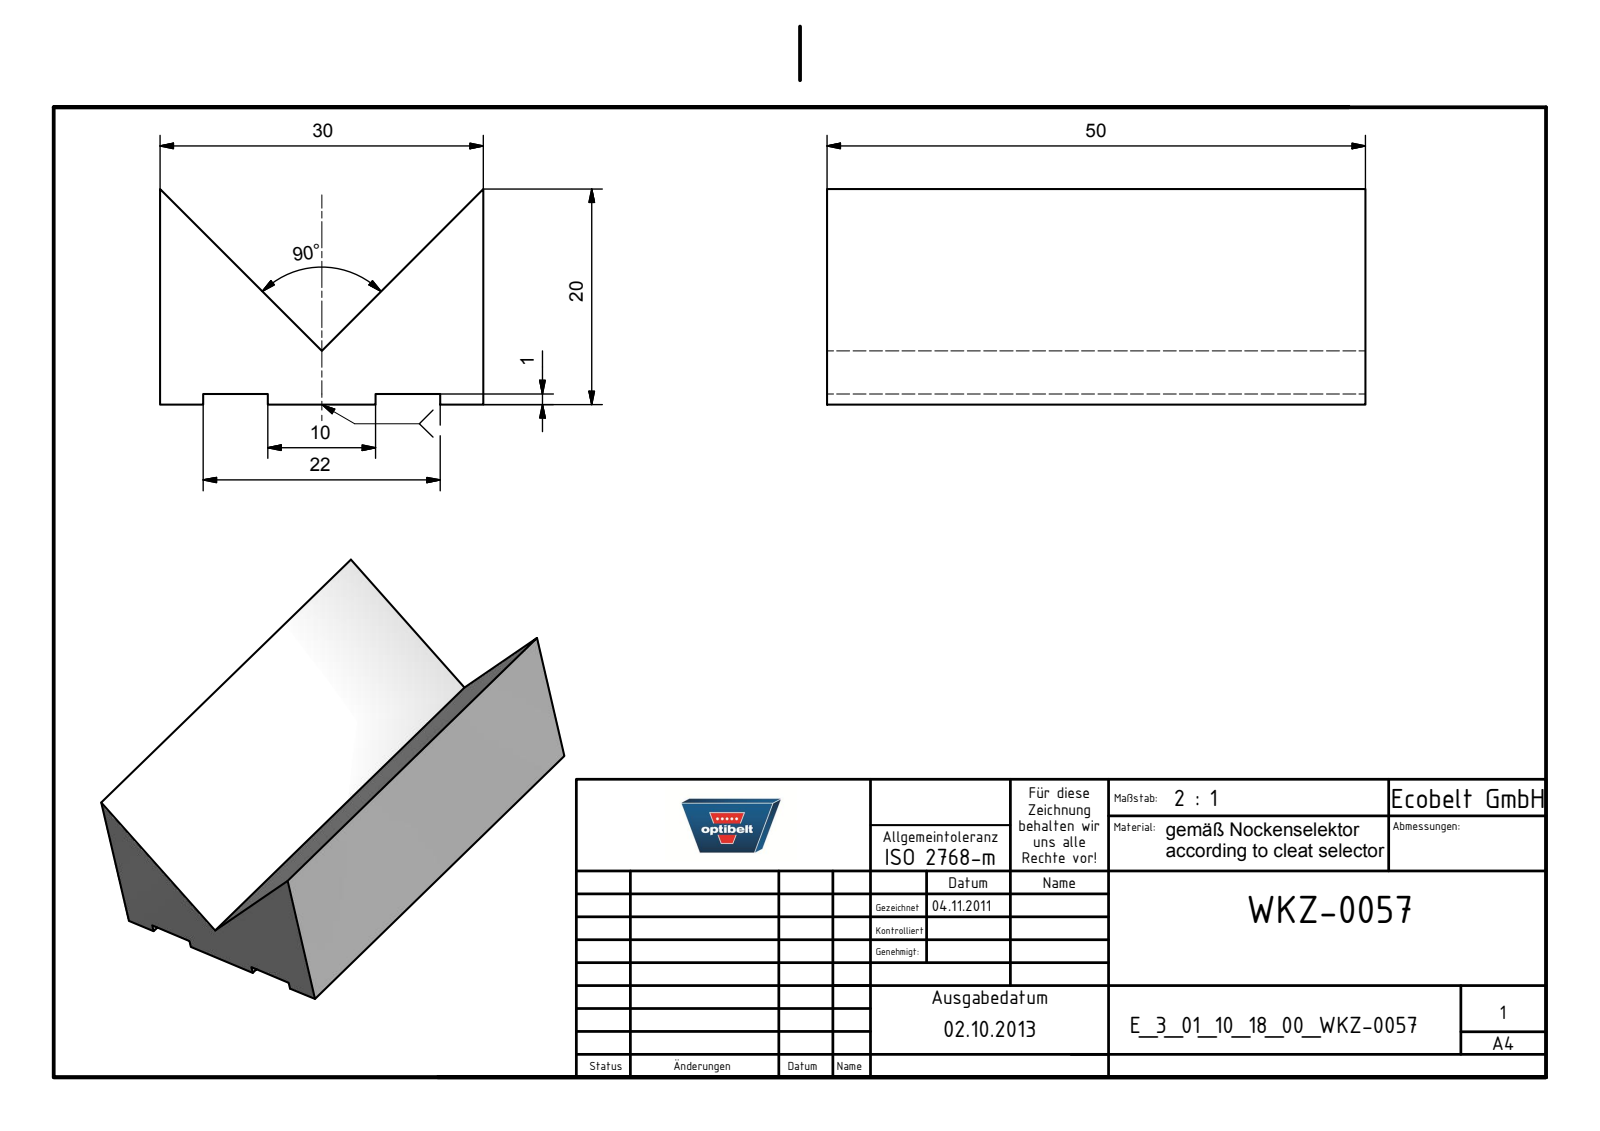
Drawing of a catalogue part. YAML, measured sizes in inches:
part_name: "E_3_01_10_18_00_WKZ-0057"
step_written_by: "Autodesk Inventor 2025 (AUTOMOTIVE_DESIGN)"
units: inches
bodies: {solids: 1, faces: 15, planar: 15, cylindrical: 0, other: 0}
overall_size: [1.969, 1.181, 0.787]
volume: 1.108
surface_area: 10.15
face_to_face_distances: [1.181, 0.039, 1.969, 0.394, 0.157, 0.787, 1.024, 0.236, 0.63, 0.866]
